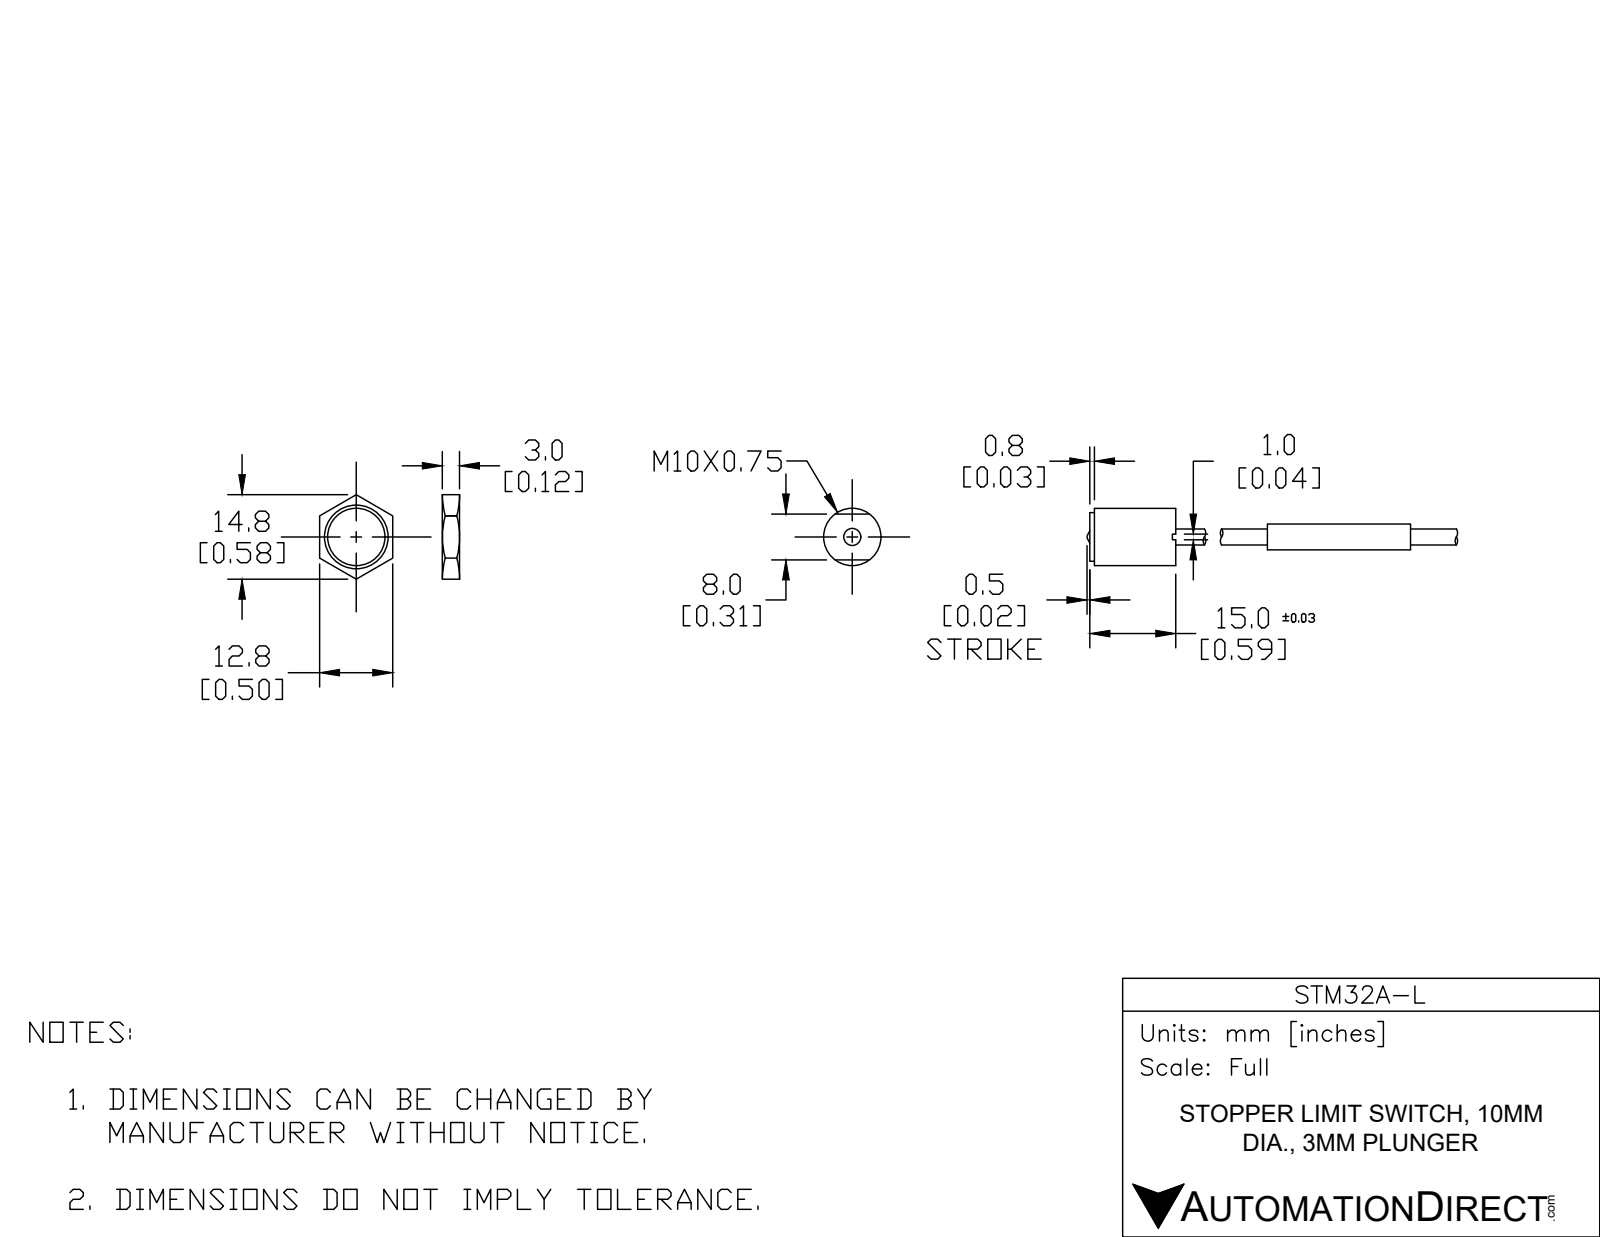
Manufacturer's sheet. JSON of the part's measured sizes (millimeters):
{"part_name": "STM32A-L", "step_written_by": "SolidWorks 2018 (CONFIG_CONTROL_DESIGN)", "units": "millimeters", "bodies": {"solids": 2, "faces": 85, "planar": 18, "cylindrical": 51, "other": 16}, "overall_size": [66.41, 10, 10], "volume_mm3": 1606, "surface_area_mm2": 1496, "round_bosses_or_shafts": [[10, 1], [4.5, 1], [2.8, 1]], "face_to_face_distances": [15, 31, 56, 16, 41, 25, 3.5, 4.5, 14.4, 0.6]}
